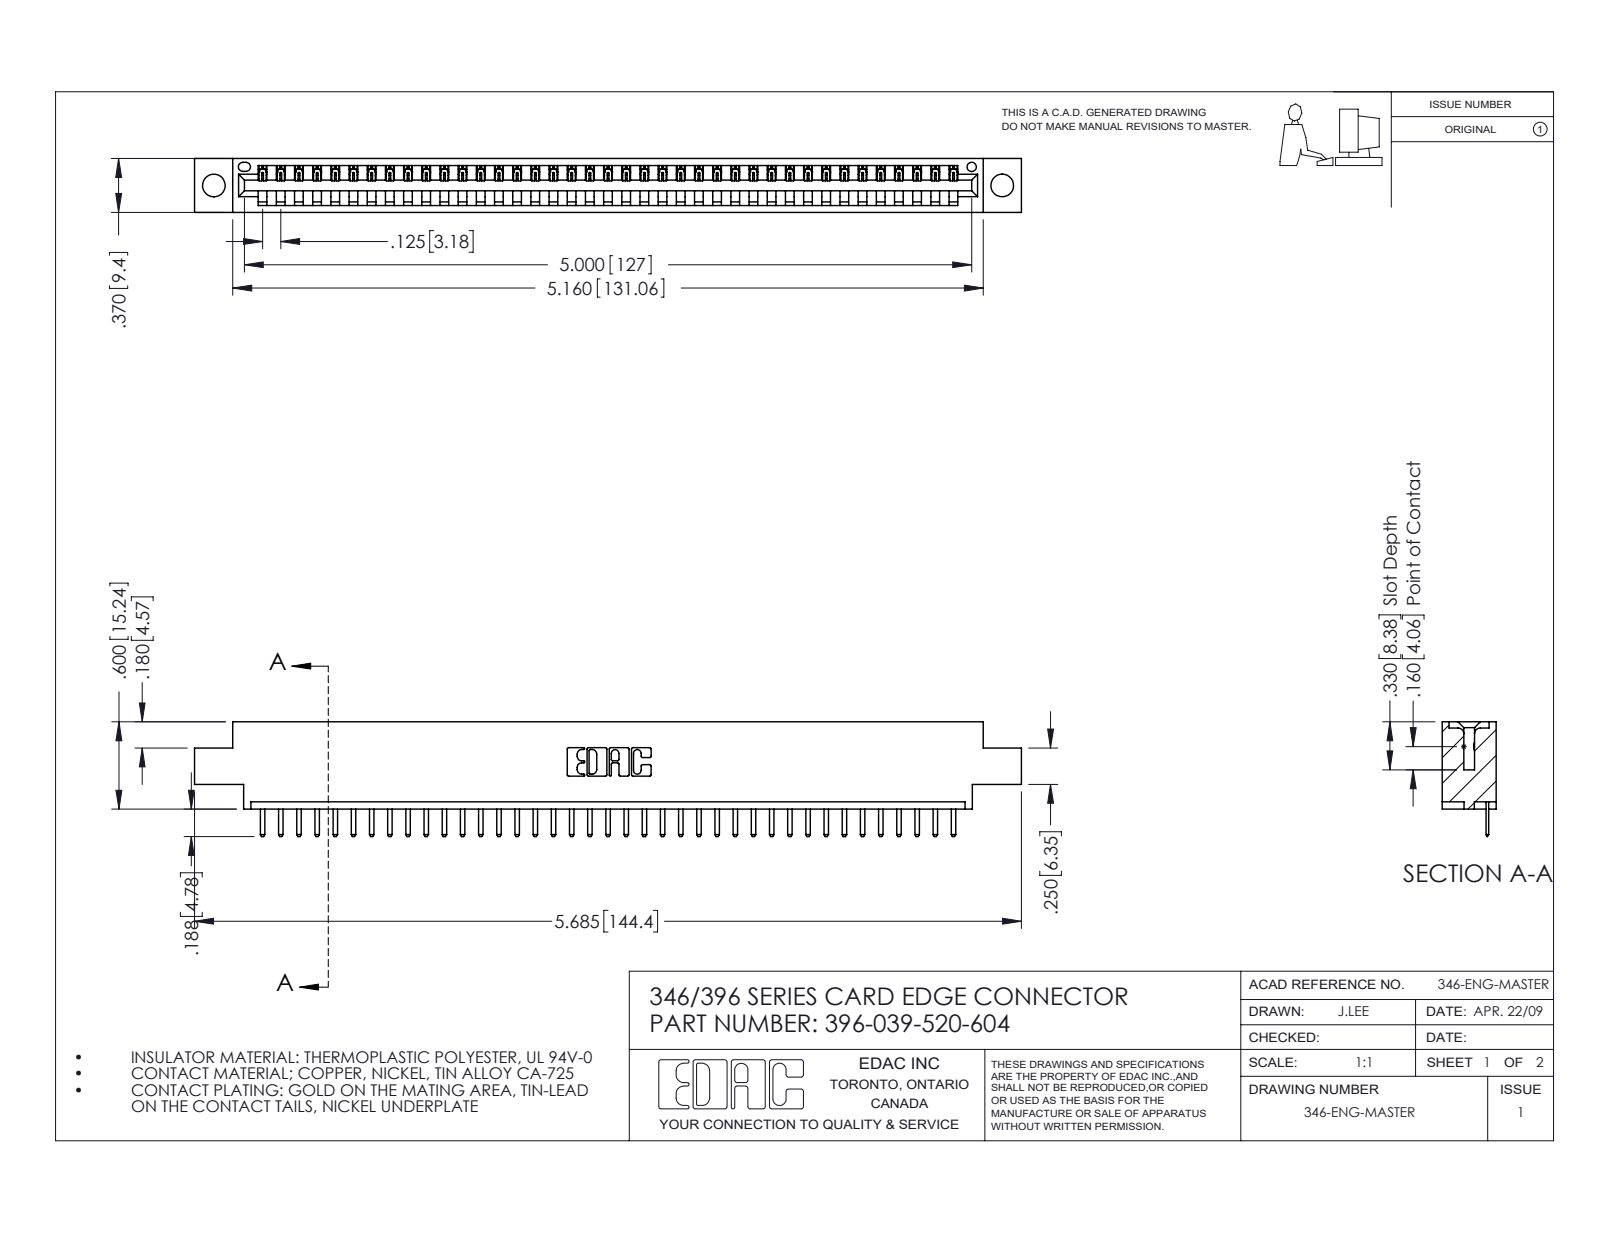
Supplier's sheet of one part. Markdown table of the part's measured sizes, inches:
| quantity | value |
| --- | --- |
| part name | 346 Part_0.170 Offset - 0.156 Dia-TH; 345-292-001_345-293-120; 396-039-520-604 |
| STEP written by | SolidWorks 2016 (CONFIG_CONTROL_DESIGN) |
| units | inches |
| bodies | 40 solids, 2544 faces (1718 planar, 826 cylindrical, 0 other) |
| overall size | 5.685 × 0.788 × 0.37 |
| volume | 0.821 in³ |
| surface area | 25.37 in² |
| round holes (diameter × count) | 0.156 × 2, 0.064 × 1 |
| partial cylindrical surfaces (radius × count) | 0.01 × 80, 0.006 × 78, 0.01 × 22, 0.007 × 6, 0.031 × 6, 0.026 × 3, 0.031 × 2, 0.04 × 2 |
| main face-to-face distances | 0.048, 0.322, 0.37, 0.25, 0.148, 0.222, 0.1, 0.174, 0.072, 0.298 |
| hole center spacings | 0.246, 5.211, 5.42 |
